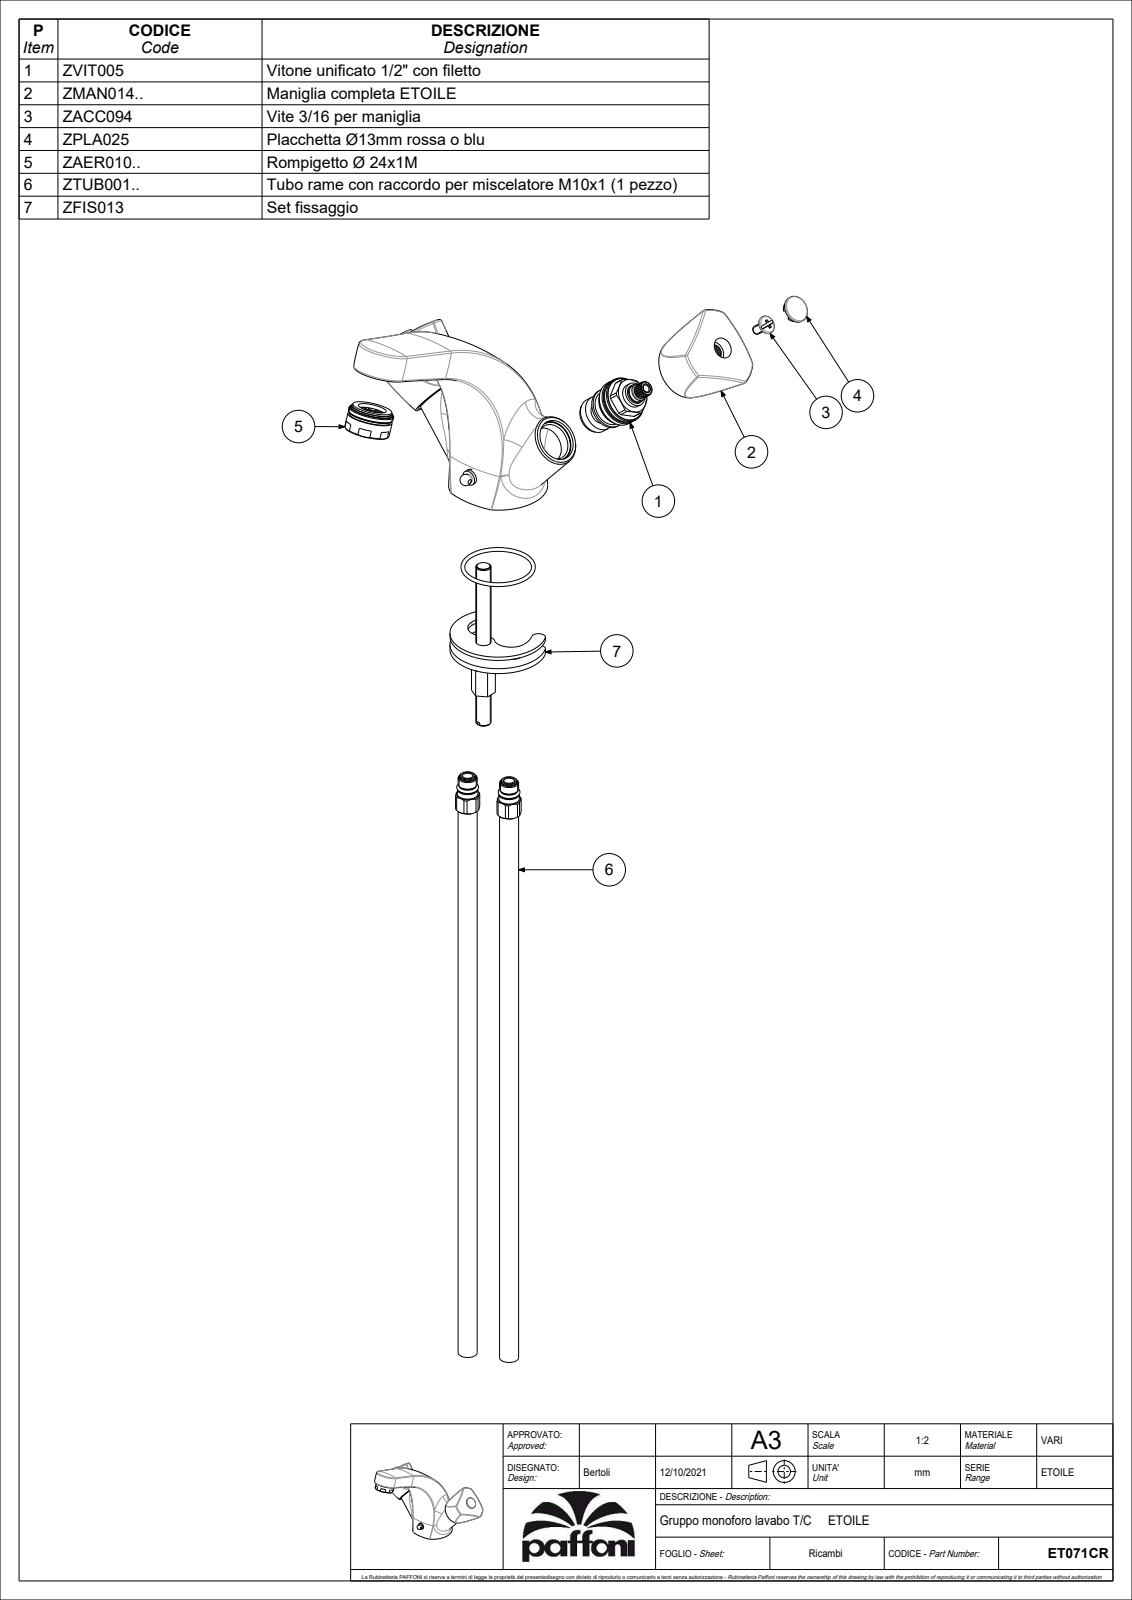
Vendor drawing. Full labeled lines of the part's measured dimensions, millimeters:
Part name (STEP PRODUCT): ET071CR
STEP written by: CREO PARAMETRIC BY PTC INC, 2020044 (CONFIG_CONTROL_DESIGN)
Units: millimetres
Bodies: 1 solid, 513 faces (143 planar, 133 cylindrical, 237 other)
Overall size (bounding box): 154.04 × 133.74 × 128.34
Volume: 151 898 mm³ · Surface area: 75 353 mm²
Round holes (diameter × count): ⌀8 ×2, ⌀9 ×2, ⌀11 ×2, ⌀29.6 ×2, ⌀2.5 ×1, ⌀4.8 ×1, ⌀6 ×1, ⌀7 ×1, ⌀15 ×1, ⌀16 ×1, ⌀19 ×1, ⌀24.5 ×1
Round bosses / shafts (diameter × count): ⌀24 ×2, ⌀22.5 ×2, ⌀18.6 ×2, ⌀17.3 ×2, ⌀14 ×2, ⌀12.5 ×2, ⌀11.5 ×2, ⌀9 ×2
Partial cylindrical surfaces — rounded edges, fillets, slot ends (radius × count): R1 ×4, R3 ×2, R5 ×2, R8 ×2, R10 ×2, R15 ×2, R1.85 ×1, R3.4 ×1
Main face-to-face distances: 9, 6, 23, 1.5, 15, 29, 40.81, 24, 25.5, 46.81
Hole centre spacings: 7.5, 11.72, 14.15, 9, 12, 15, 21
